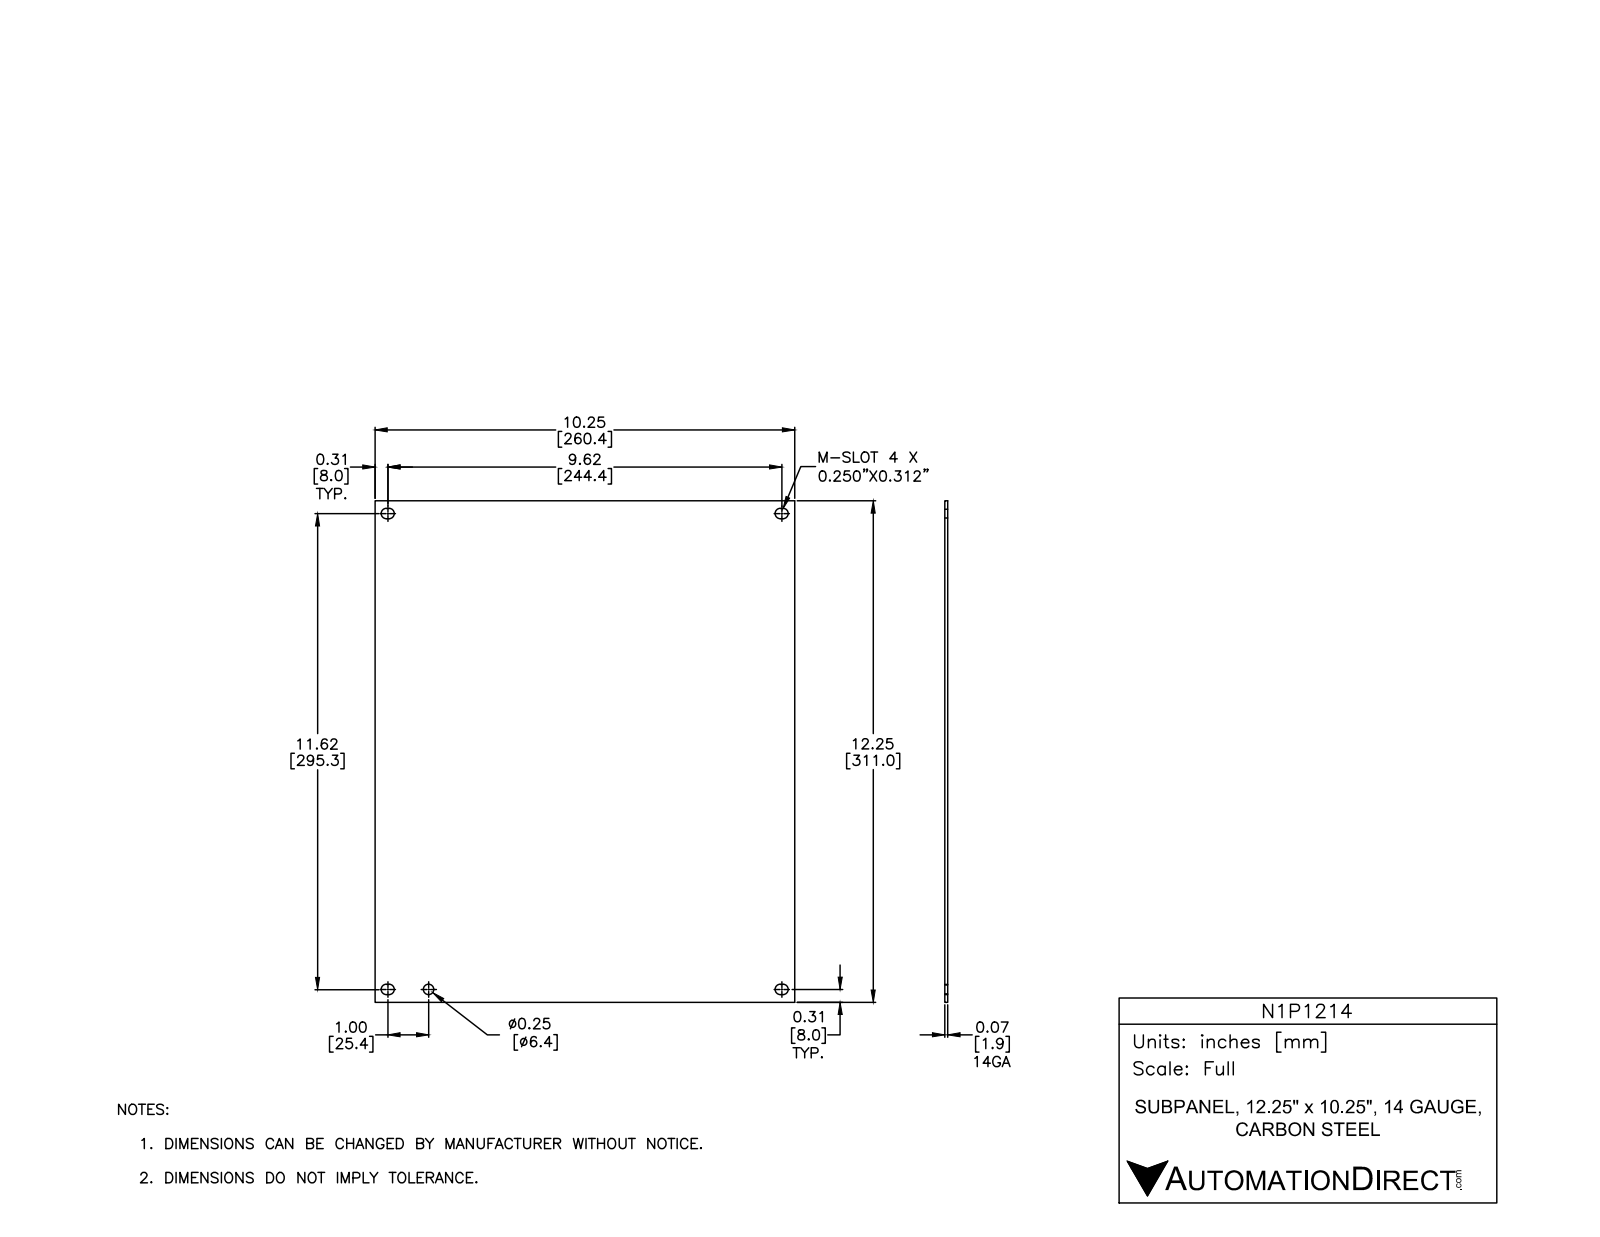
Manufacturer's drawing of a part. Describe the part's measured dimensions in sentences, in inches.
The part is named "N1P1214". Its 3-D file was written by "Autodesk Inventor 2012 (AUTOMOTIVE_DESIGN)". It is 1 solid with 23 faces: 14 planar, 9 cylindrical and 0 other. Overall it measures 12.25 by 10.25 by 0.074 inches. Its volume is 9.269 cubic inches and its surface area 254.2 square inches. Round holes: 1 of diameter 0.25. Partial cylindrical surfaces (rounded edges, fillets, slot ends): 8 of radius 0.125. The main face-to-face distances are 0.074, 10.25, 12.25, 0.438, 11.812, 0.188, 12.062, 0.25, 11.624, 11.374.
